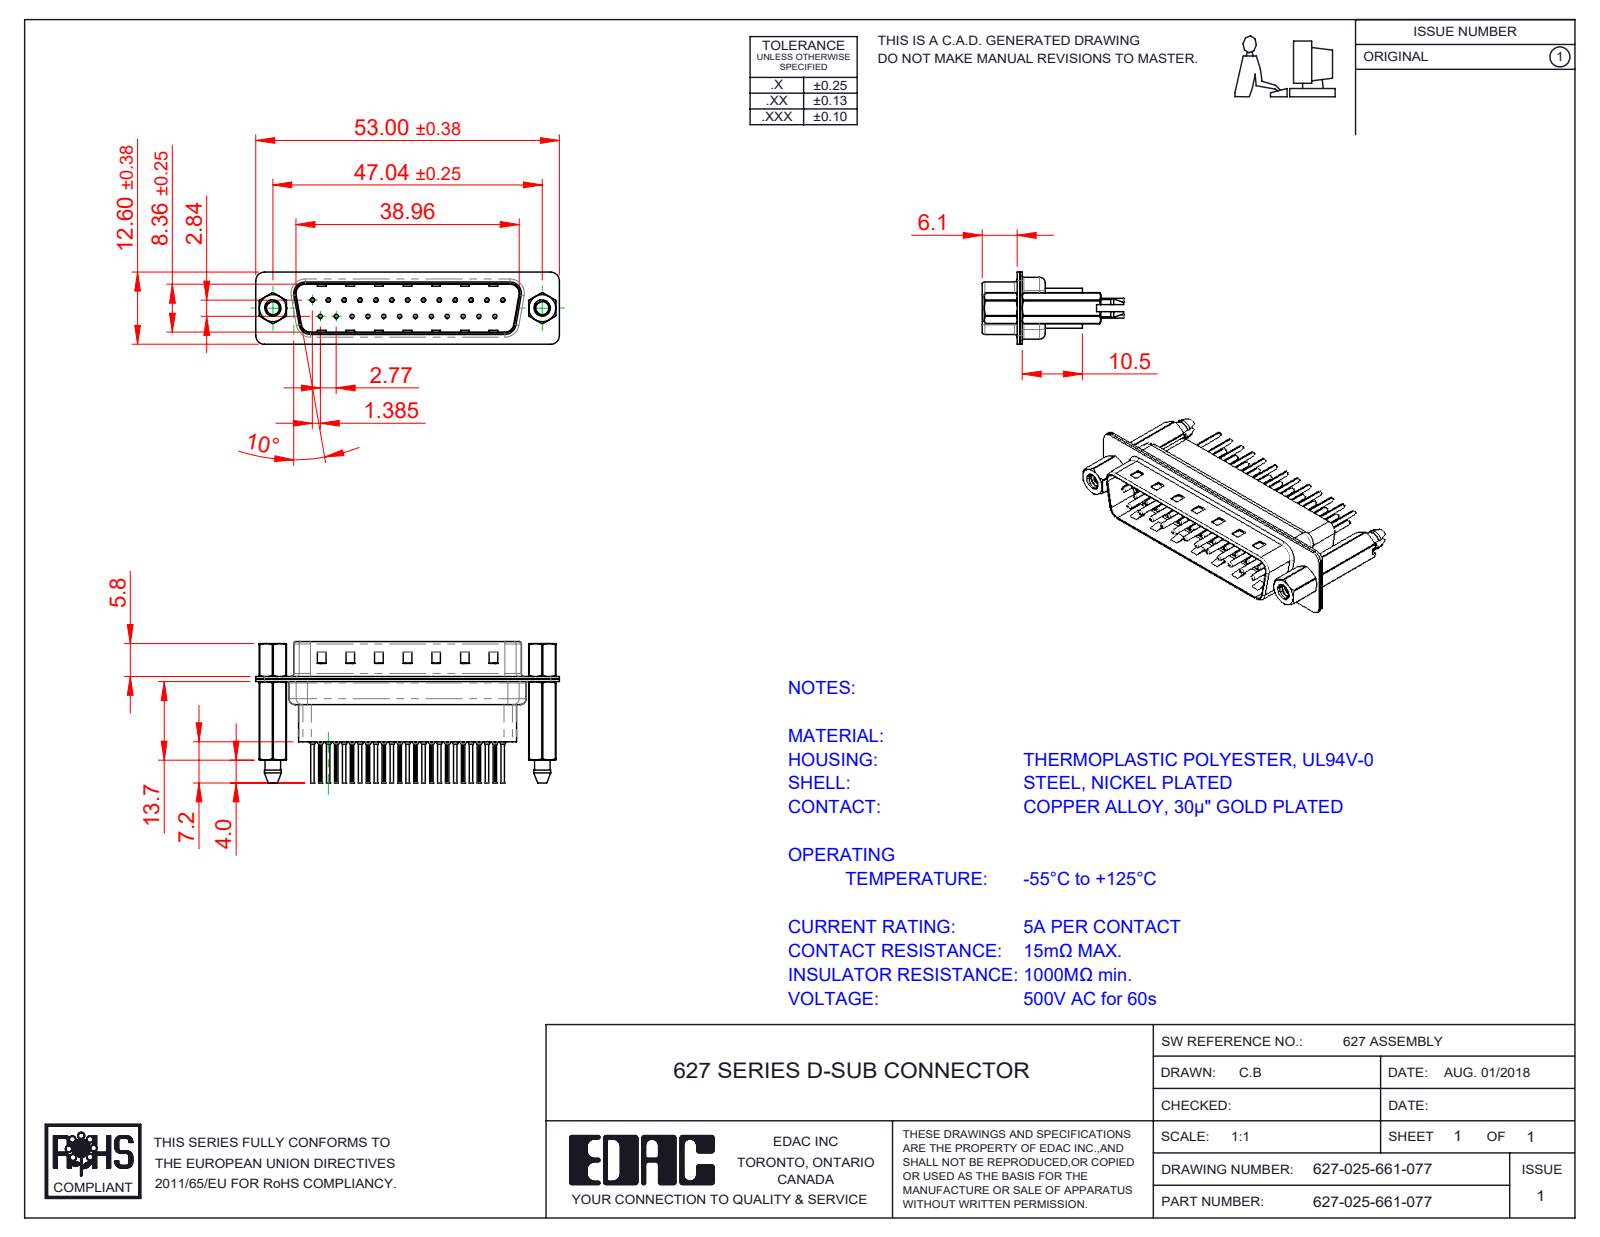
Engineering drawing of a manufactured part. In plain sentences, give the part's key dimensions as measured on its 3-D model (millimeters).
The part is named "627 Shell Front_25 Contacts; 627 Contact Row 1_61; 627 4-40 Threaded Boardlock_HP61; 627 Housing_25 HP (+4 more)". Its 3-D file was written by "SolidWorks 2020 (CONFIG_CONTROL_DESIGN)". It is 32 solids with 3060 faces: 825 planar, 1200 cylindrical and 1035 other. Overall it measures 53 by 24.6 by 12.6 millimeters. Its volume is 4 376 cubic millimeters and its surface area 11 253 square millimeters. Round holes: 25 of diameter 0.2, 25 of diameter 0.35, 25 of diameter 1.1, 25 of diameter 1.6, 2 of diameter 2.26, 2 of diameter 2.29, 2 of diameter 4, 2 of diameter 4.8. Round bosses or shafts: 25 of diameter 2, 25 of diameter 1.5, 25 of diameter 0.75, 25 of diameter 0.6, 2 of diameter 4.9, 2 of diameter 2.79. Partial cylindrical surfaces (rounded edges, fillets, slot ends): 50 of radius 0.1, 18 of radius 1.5, 12 of radius 2, 10 of radius 1.6, 8 of radius 0.5, 4 of radius 0.25, 4 of radius 0.6, 4 of radius 0.65. The main face-to-face distances are 0.4, 0.45, 0.82, 9.58, 0.68, 7.68, 1.5, 0.9, 1.08, 8.08. The hole center spacings are 3.16, 8.31, 2.77, 5.54, 11.08, 16.62, 5.03, 5.04.
